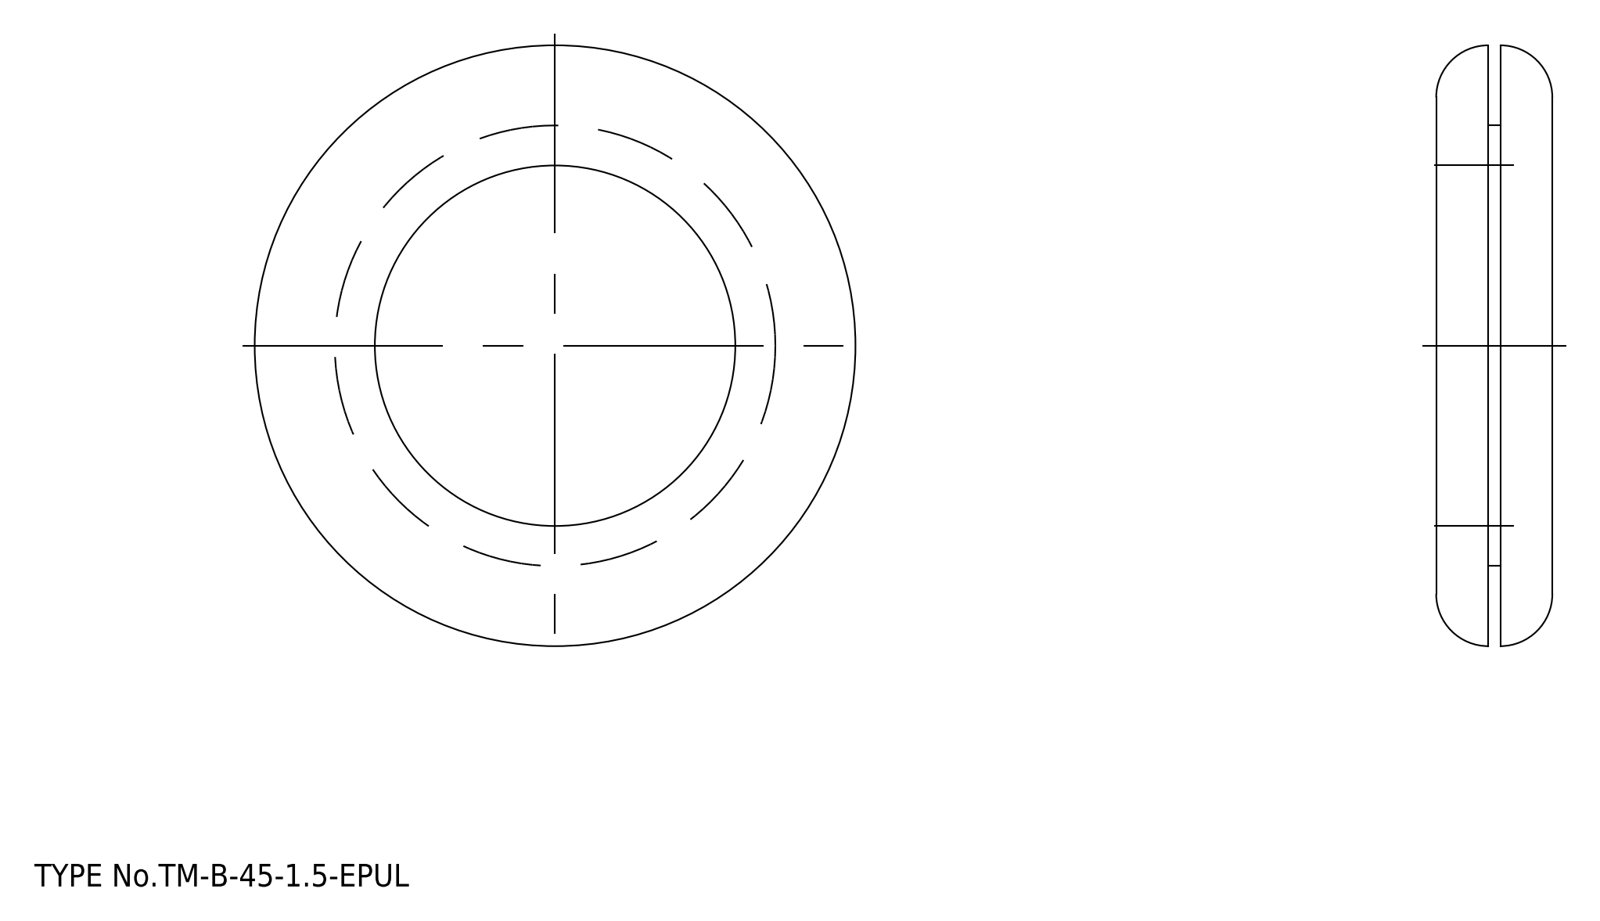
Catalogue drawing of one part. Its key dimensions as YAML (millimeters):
step_written_by: "spGate 15.6.1 (AUTOMOTIVE_DESIGN)"
units: millimeters
bodies: {solids: 1, faces: 12, planar: 4, cylindrical: 4, other: 4}
overall_size: [75, 75, 14.5]
volume: 33854
surface_area: 13765
round_holes:
  - {diameter: 45, count: 1}
round_bosses_or_shafts:
  - {diameter: 55, count: 1}
face_to_face_distances: [6.5, 8, 1.5, 14.5]
